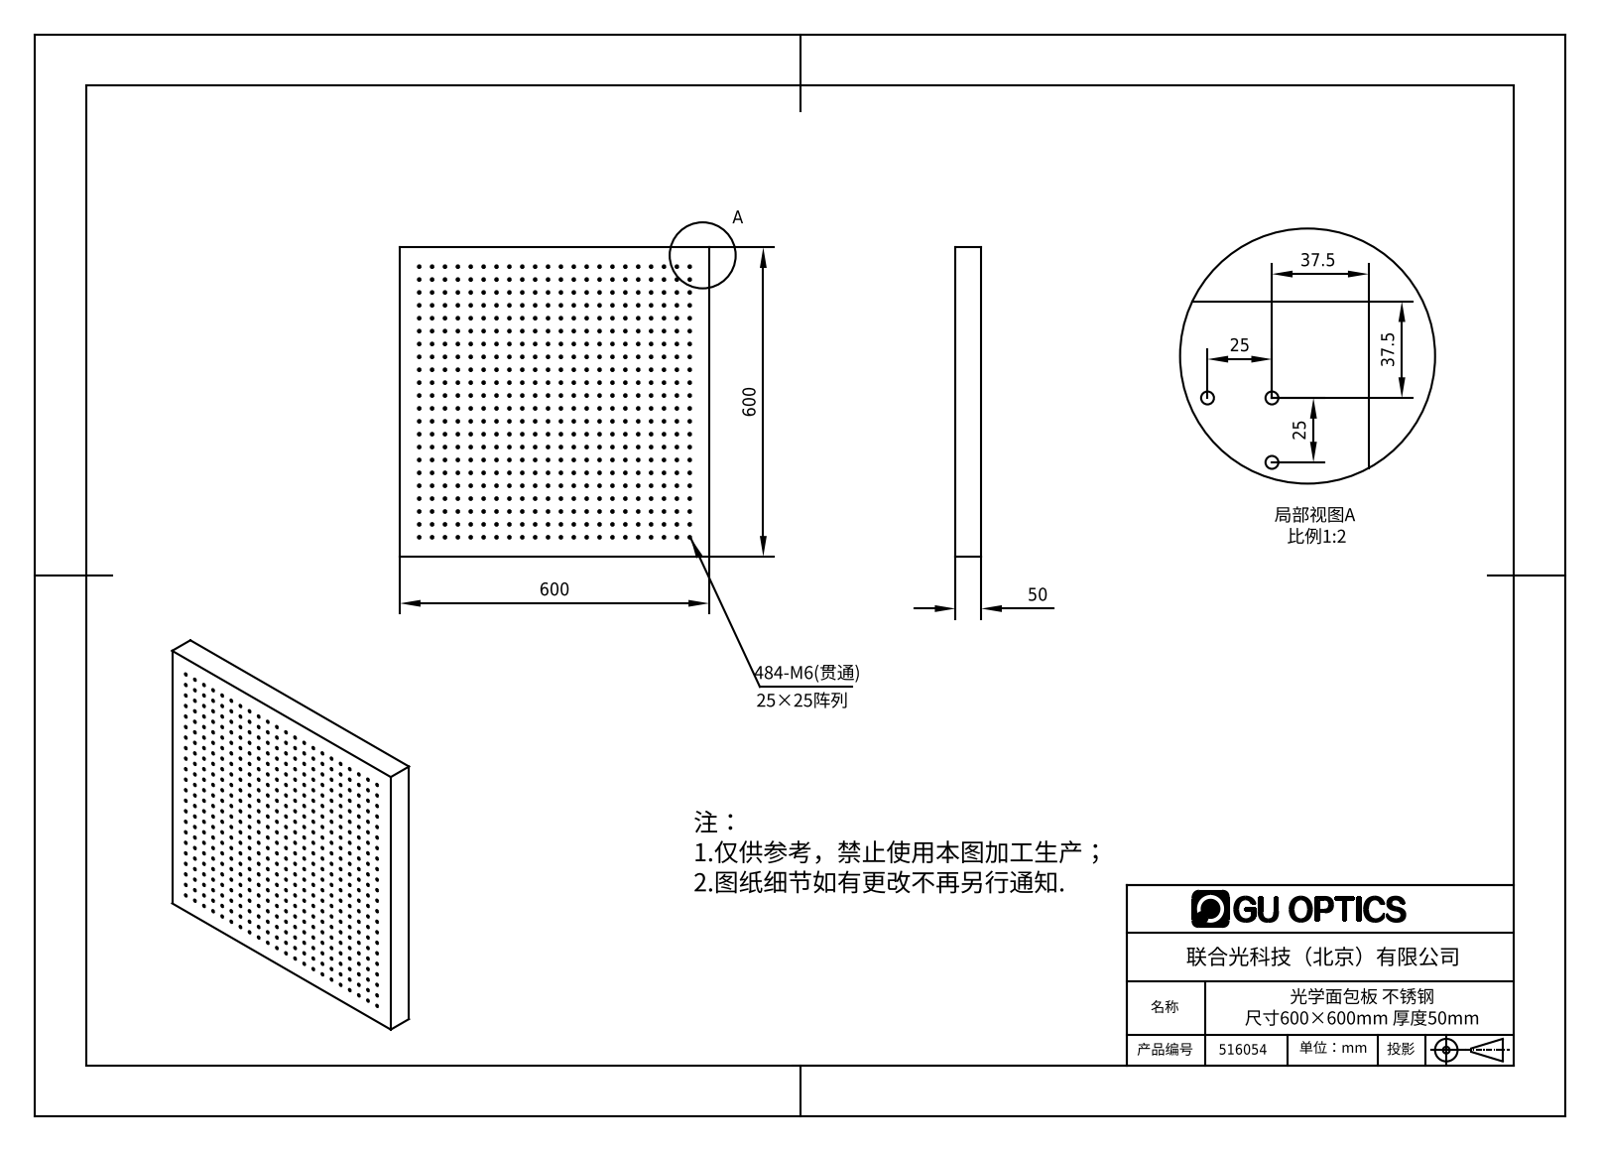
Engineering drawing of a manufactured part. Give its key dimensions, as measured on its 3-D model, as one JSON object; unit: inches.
{"part_name": "516054", "step_written_by": "SolidWorks 2016 (AUTOMOTIVE_DESIGN)", "units": "inches", "bodies": {"solids": 1, "faces": 974, "planar": 6, "cylindrical": 968, "other": 0}, "overall_size": [23.622, 23.622, 1.969], "volume_in3": 1069, "surface_area_in2": 1862, "round_holes": [[0.197, 484]], "face_to_face_distances": [1.969, 23.622], "hole_center_spacings": [0.984, 1.969, 2.953, 3.937, 2.201, 4.921, 1.392, 5.906]}
